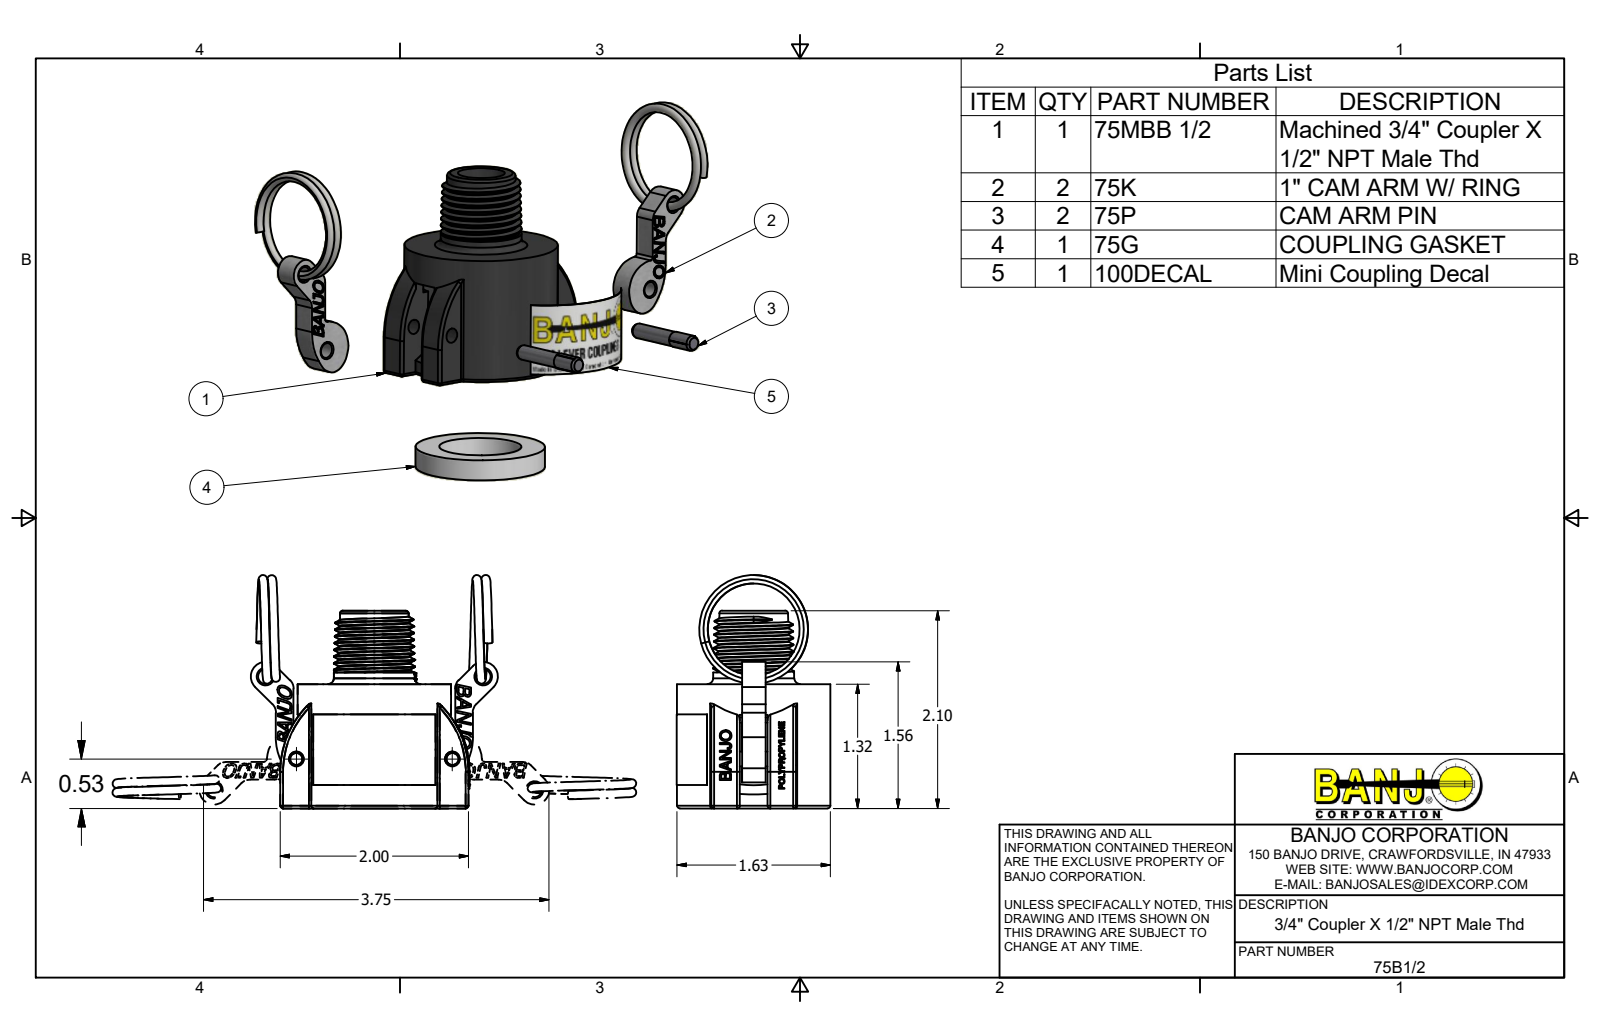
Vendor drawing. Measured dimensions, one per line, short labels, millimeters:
name: 75B050; 75B050U; 75MBB050; 75BB050 (+6 more)
written by: Autodesk Inventor 2017 (AUTOMOTIVE_DESIGN)
unit: mm
bodies: 9 solids, 807 faces (402 planar, 94 cylindrical, 311 other)
size: 66.69 × 62.97 × 41.47
volume: 33 425 mm³; area: 23 241 mm²
holes: 4× ⌀3.96, 2× ⌀4.04, 1× ⌀12.7, 1× ⌀22.22, 1× ⌀32.61, 1× ⌀36.12
bosses: 2× ⌀4.17, 1× ⌀41.4, 1× ⌀34.92, 1× ⌀21.84
rounds: 18× R0.76, 4× R3.17, 2× R0.79, 2× R3.97, 2× R15.08, 1× R2.54, 1× R5.9, 1× R11.18
face distances: 4.85, 6.35, 5.53, 10.38, 7.68, 15.18, 0.51, 0.64, 6.86, 14.67
hole spacings: 23.74, 55.1, 42.09, 58.75
